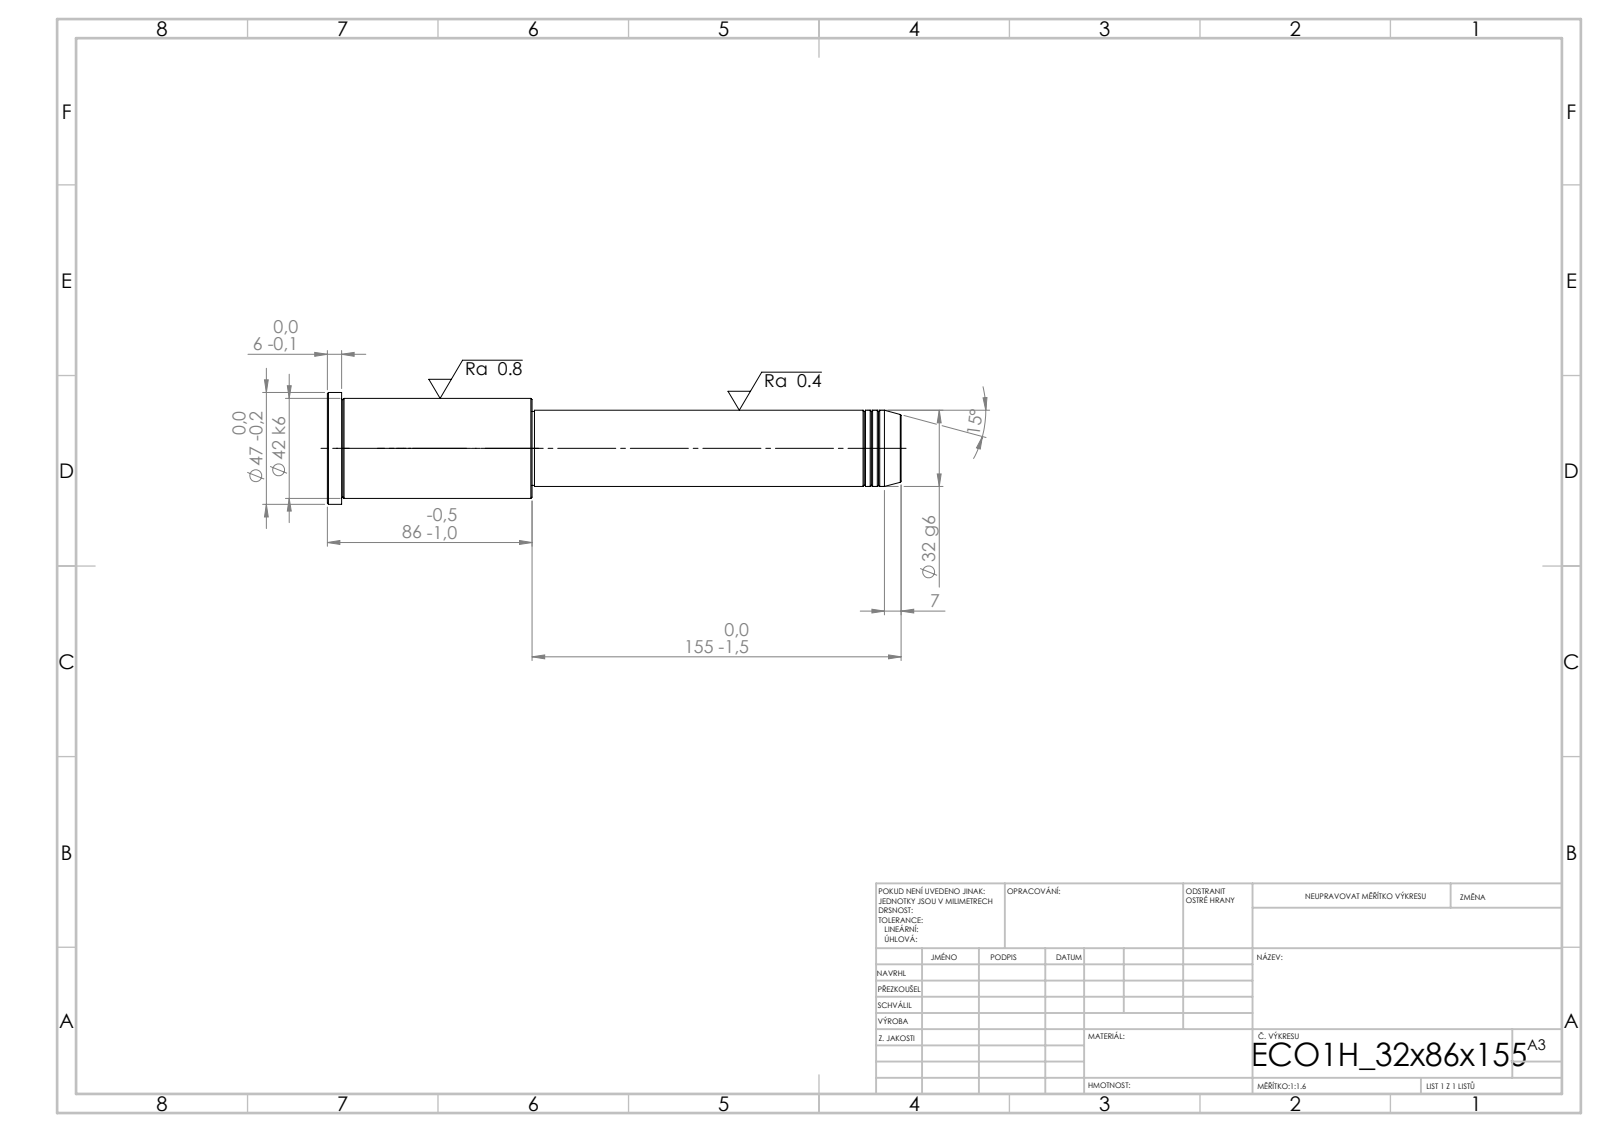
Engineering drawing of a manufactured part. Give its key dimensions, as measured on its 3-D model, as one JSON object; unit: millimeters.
{"step_written_by": "SolidWorks 2019 (CONFIG_CONTROL_DESIGN)", "units": "millimeters", "bodies": {"solids": 1, "faces": 43, "planar": 5, "cylindrical": 14, "other": 24}, "overall_size": [241, 47, 47], "volume_mm3": 245014, "surface_area_mm2": 30537, "round_bosses_or_shafts": [[47, 1], [42, 1], [32, 1], [31, 1]], "face_to_face_distances": [241, 155, 86, 235, 80, 6, 154, 1, 81, 87]}
